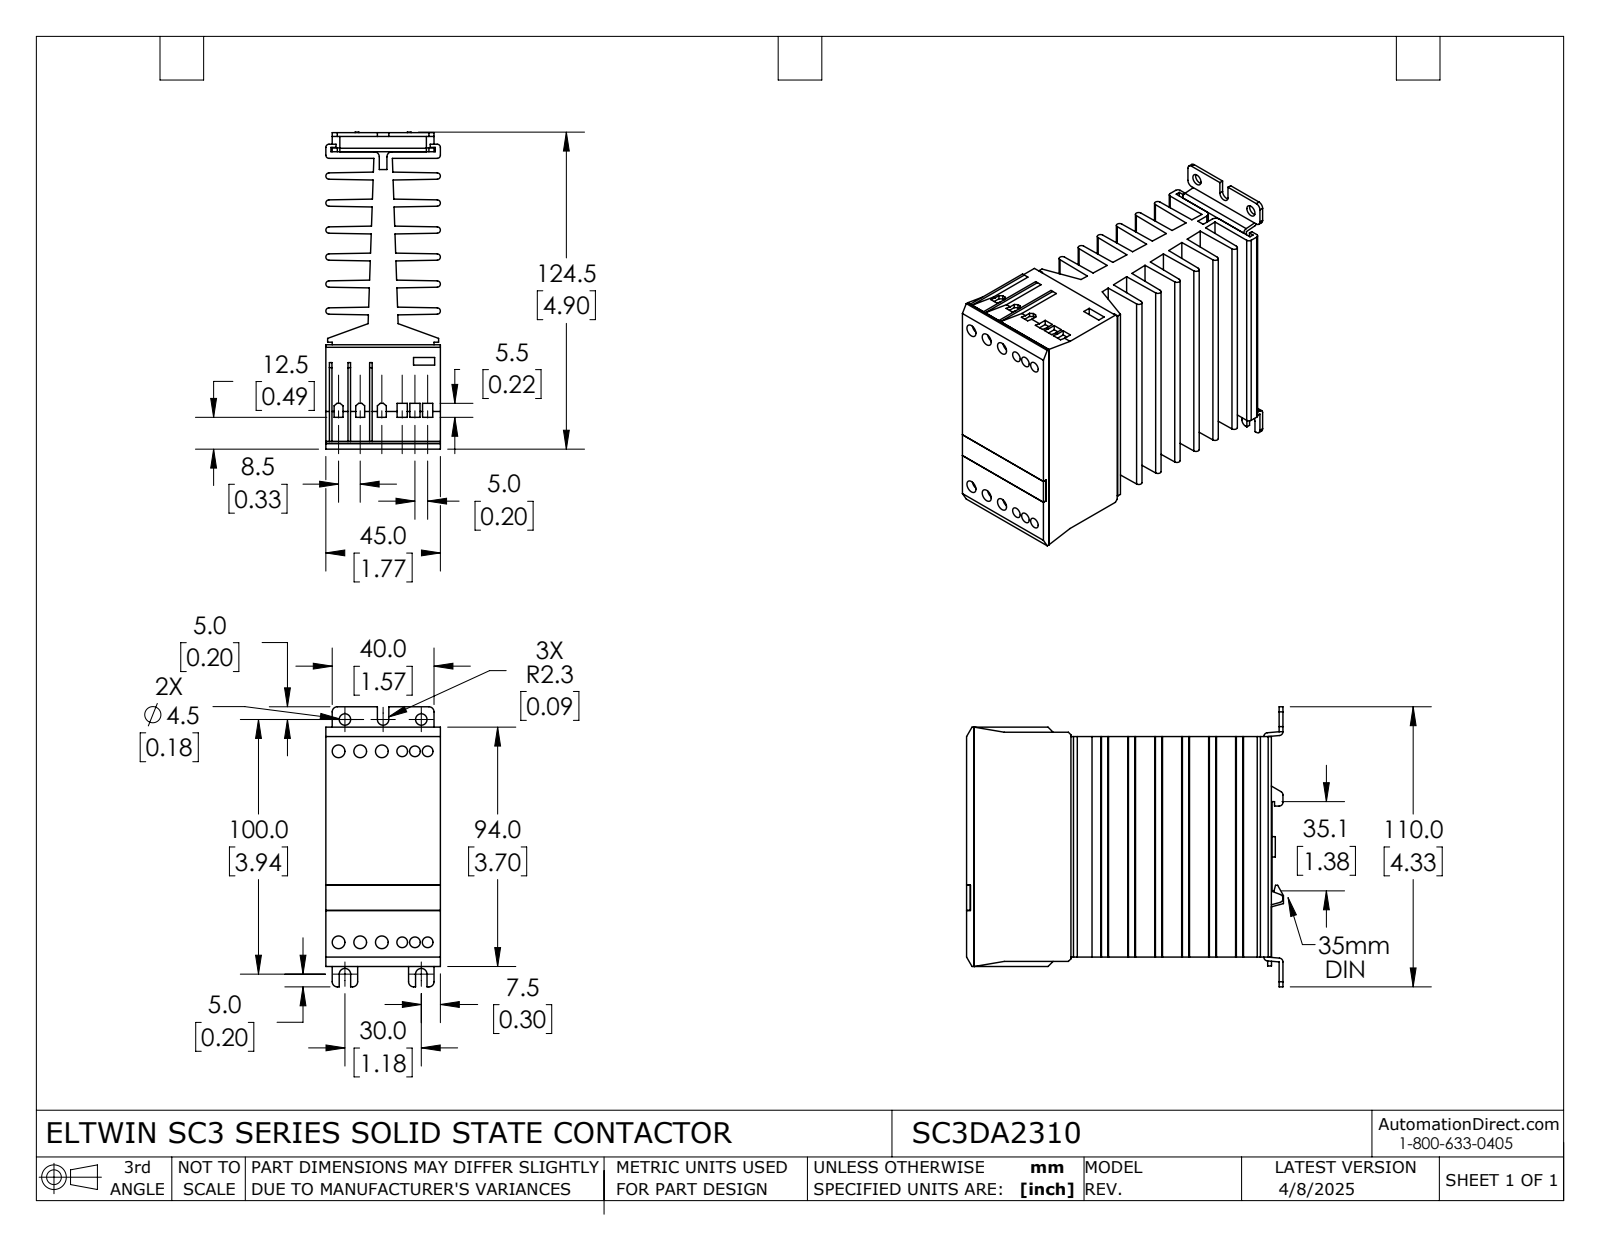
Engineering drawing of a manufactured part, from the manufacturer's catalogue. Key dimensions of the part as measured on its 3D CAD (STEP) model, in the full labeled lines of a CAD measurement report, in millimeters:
Part name (STEP PRODUCT): SC3DA2310
STEP written by: SolidWorks 2021 (AUTOMOTIVE_DESIGN)
Units: millimetres
Bodies: 5 solids, 427 faces (316 planar, 111 cylindrical, 0 other)
Overall size (bounding box): 124.5 × 110 × 45
Volume: 309 200 mm³ · Surface area: 107 000 mm²
Round holes (diameter × count): ⌀4.2 ×6, ⌀4.4 ×6, ⌀5 ×6, ⌀6 ×6, ⌀4.5 ×2
Round bosses / shafts (diameter × count): ⌀8 ×1
Partial cylindrical surfaces — rounded edges, fillets, slot ends (radius × count): R2 ×18, R1.2 ×16, R1.5 ×10, R1.3 ×4, R2.3 ×3
Main face-to-face distances: 10.6, 21.2, 3.2, 31.8, 7.4, 13.8, 18, 24.4, 42.4, 28.6
Hole centre spacings: 75, 5, 8.5, 75.2, 75.5, 12.8, 30, 87.5
